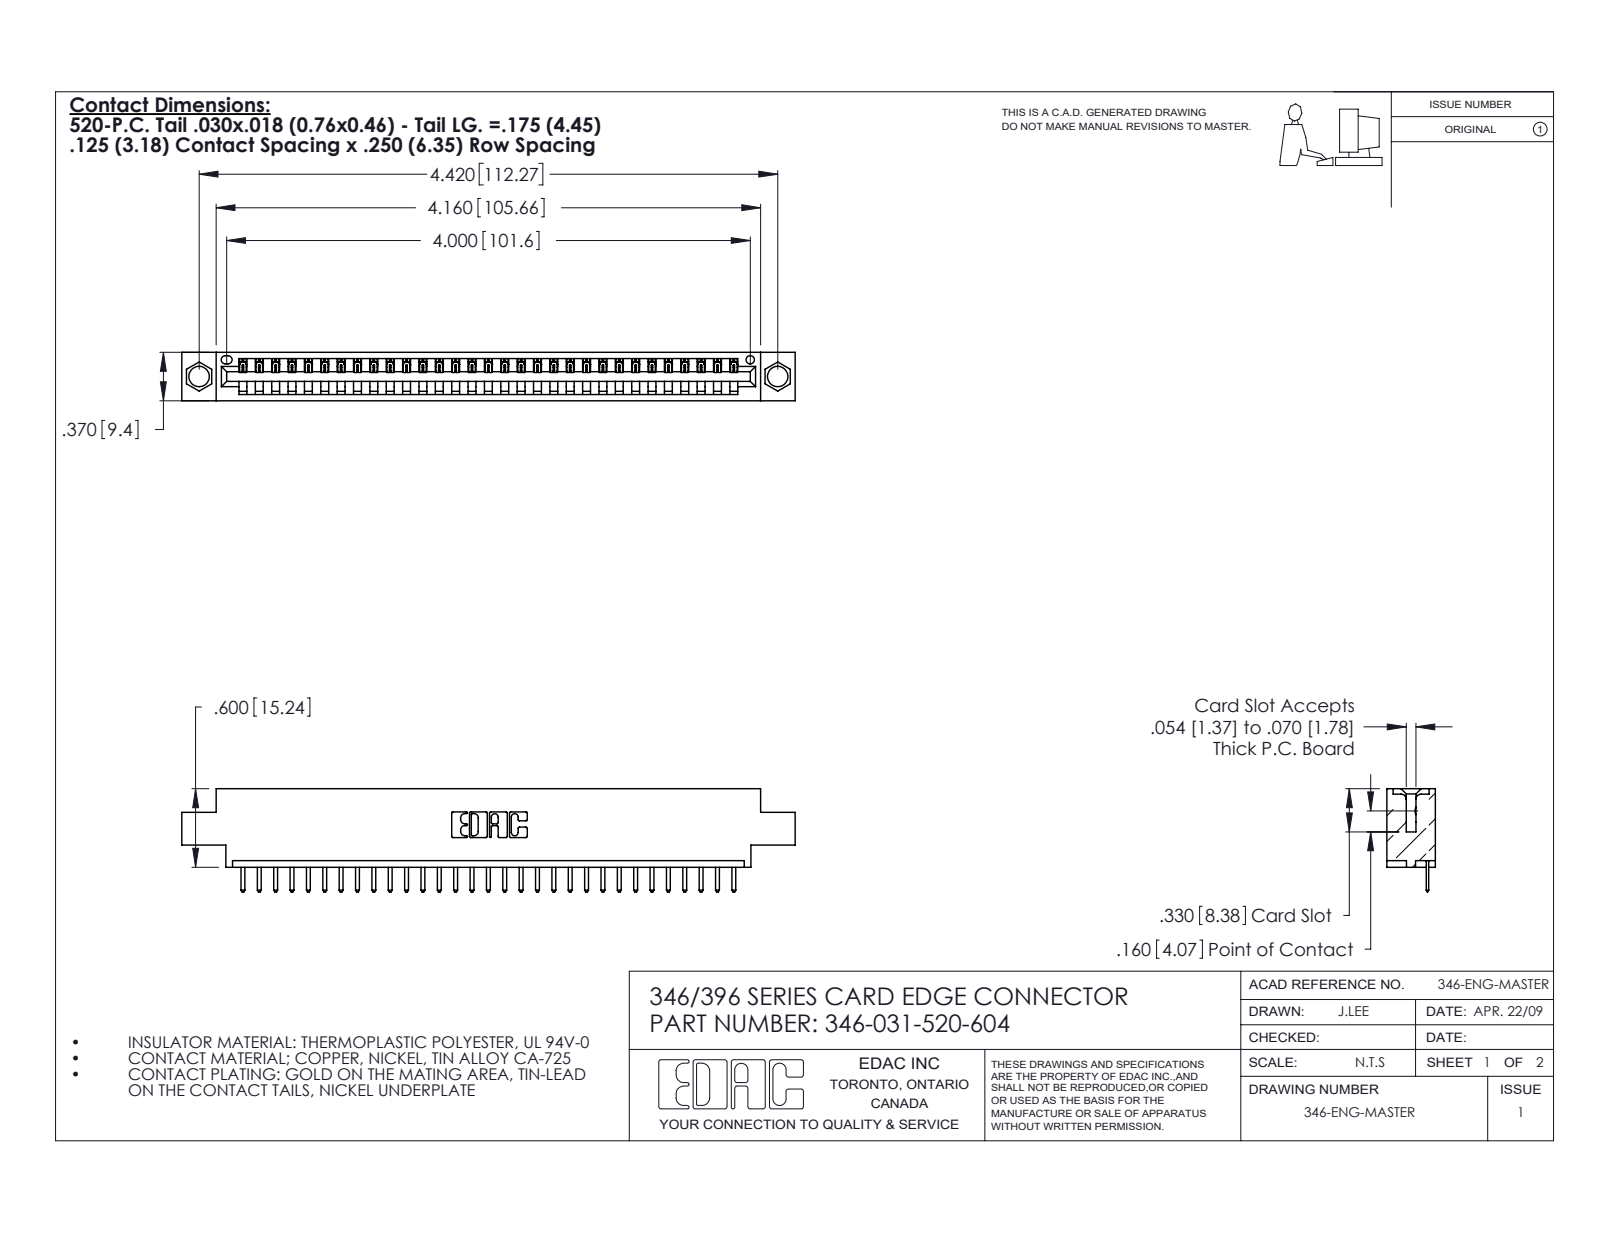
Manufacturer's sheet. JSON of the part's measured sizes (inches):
{"part_name": "346-031-520-604; 345-292-001_345-293-120; 346 Part_0.170 Offset - 0.156 Dia-TH", "step_written_by": "SolidWorks 2020 (CONFIG_CONTROL_DESIGN)", "units": "inches", "bodies": {"solids": 32, "faces": 2062, "planar": 1396, "cylindrical": 666, "other": 0}, "overall_size": [4.685, 0.788, 0.37], "volume_in3": 0.669, "surface_area_in2": 20.59, "round_holes": [[0.156, 2], [0.064, 1]], "partial_cylinders_radius": [[0.01, 64], [0.006, 62], [0.01, 22], [0.007, 6], [0.031, 6], [0.026, 3], [0.031, 2], [0.04, 2]], "face_to_face_distances": [0.048, 0.322, 0.37, 0.25, 0.222, 0.148, 0.1, 0.174, 0.072, 0.298], "hole_center_spacings": [0.246, 4.212, 4.42]}
